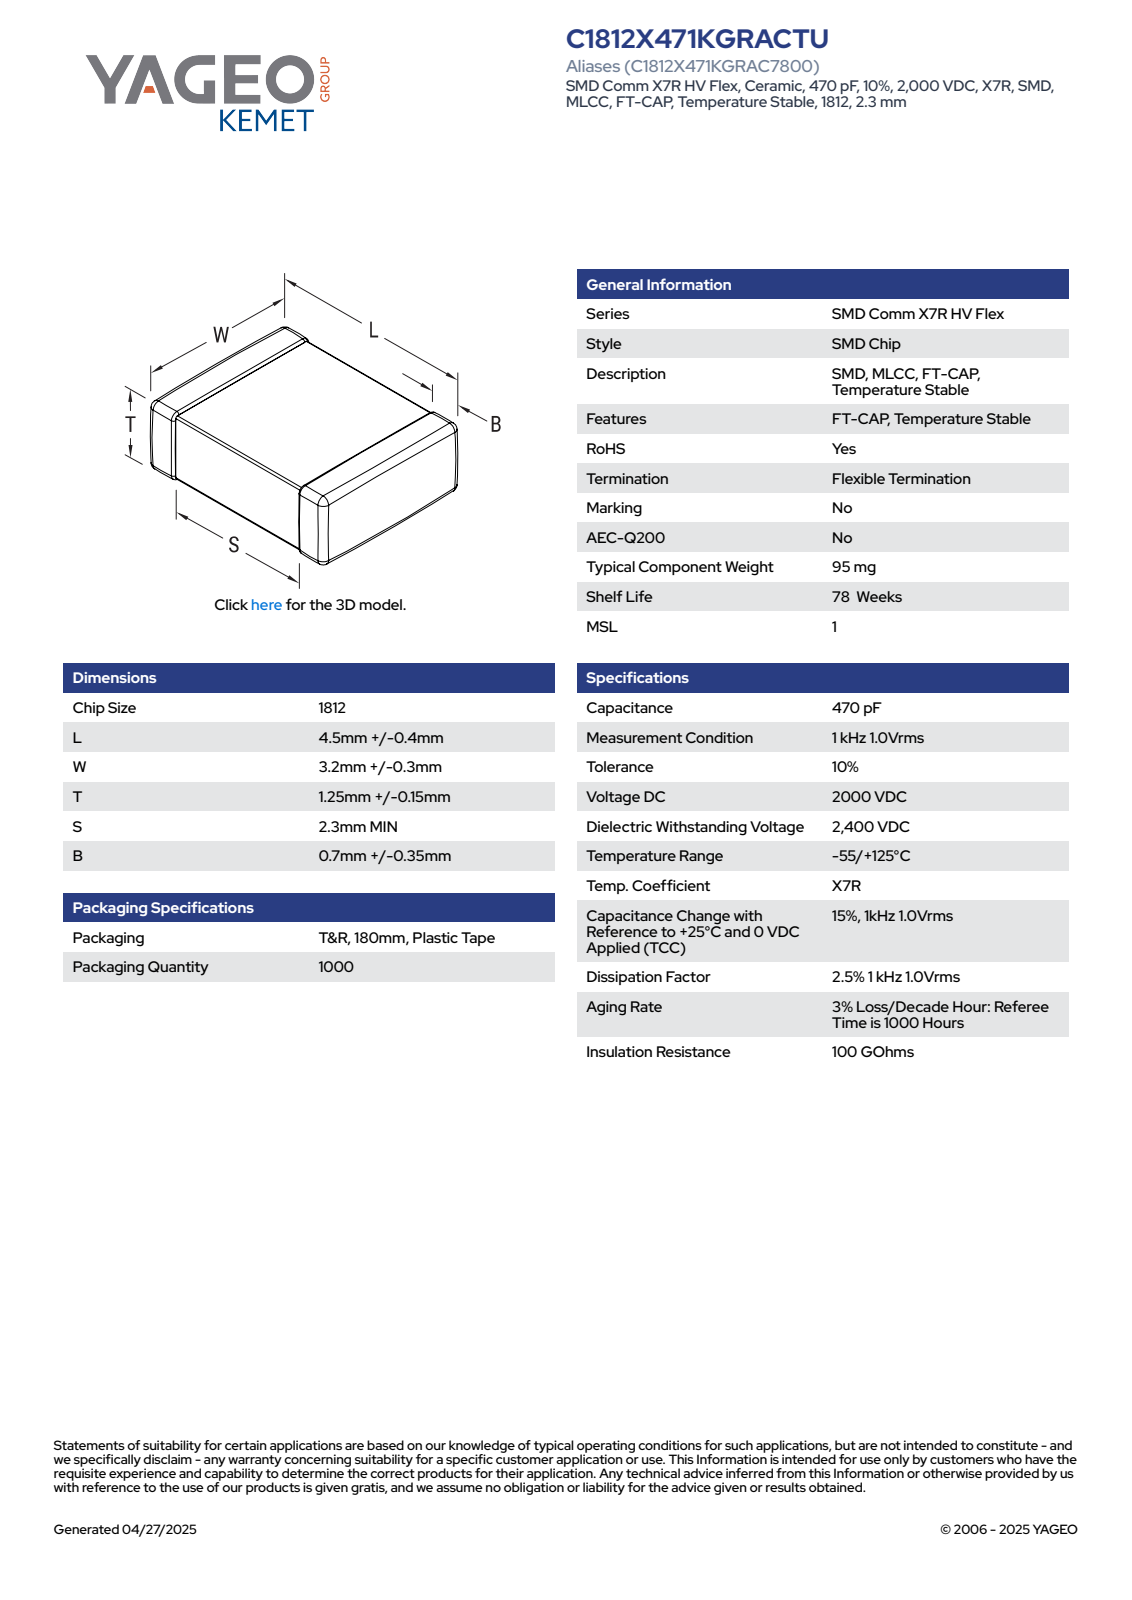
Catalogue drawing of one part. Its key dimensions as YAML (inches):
part_name: "CCS_CCSTDNOS_1812_L4.9W3.5T1.4B1.05"
step_written_by: "SolidWorks 2014 (AUTOMOTIVE_DESIGN)"
units: inches
bodies: {solids: 4, faces: 121, planar: 71, cylindrical: 34, other: 16}
overall_size: [0.193, 0.138, 0.055]
volume: 0.001
surface_area: 0.087
face_to_face_distances: [0.052, 0.05, 0.055, 0.135, 0.193, 0.132, 0.138, 0.056, 0.076, 0.059]
